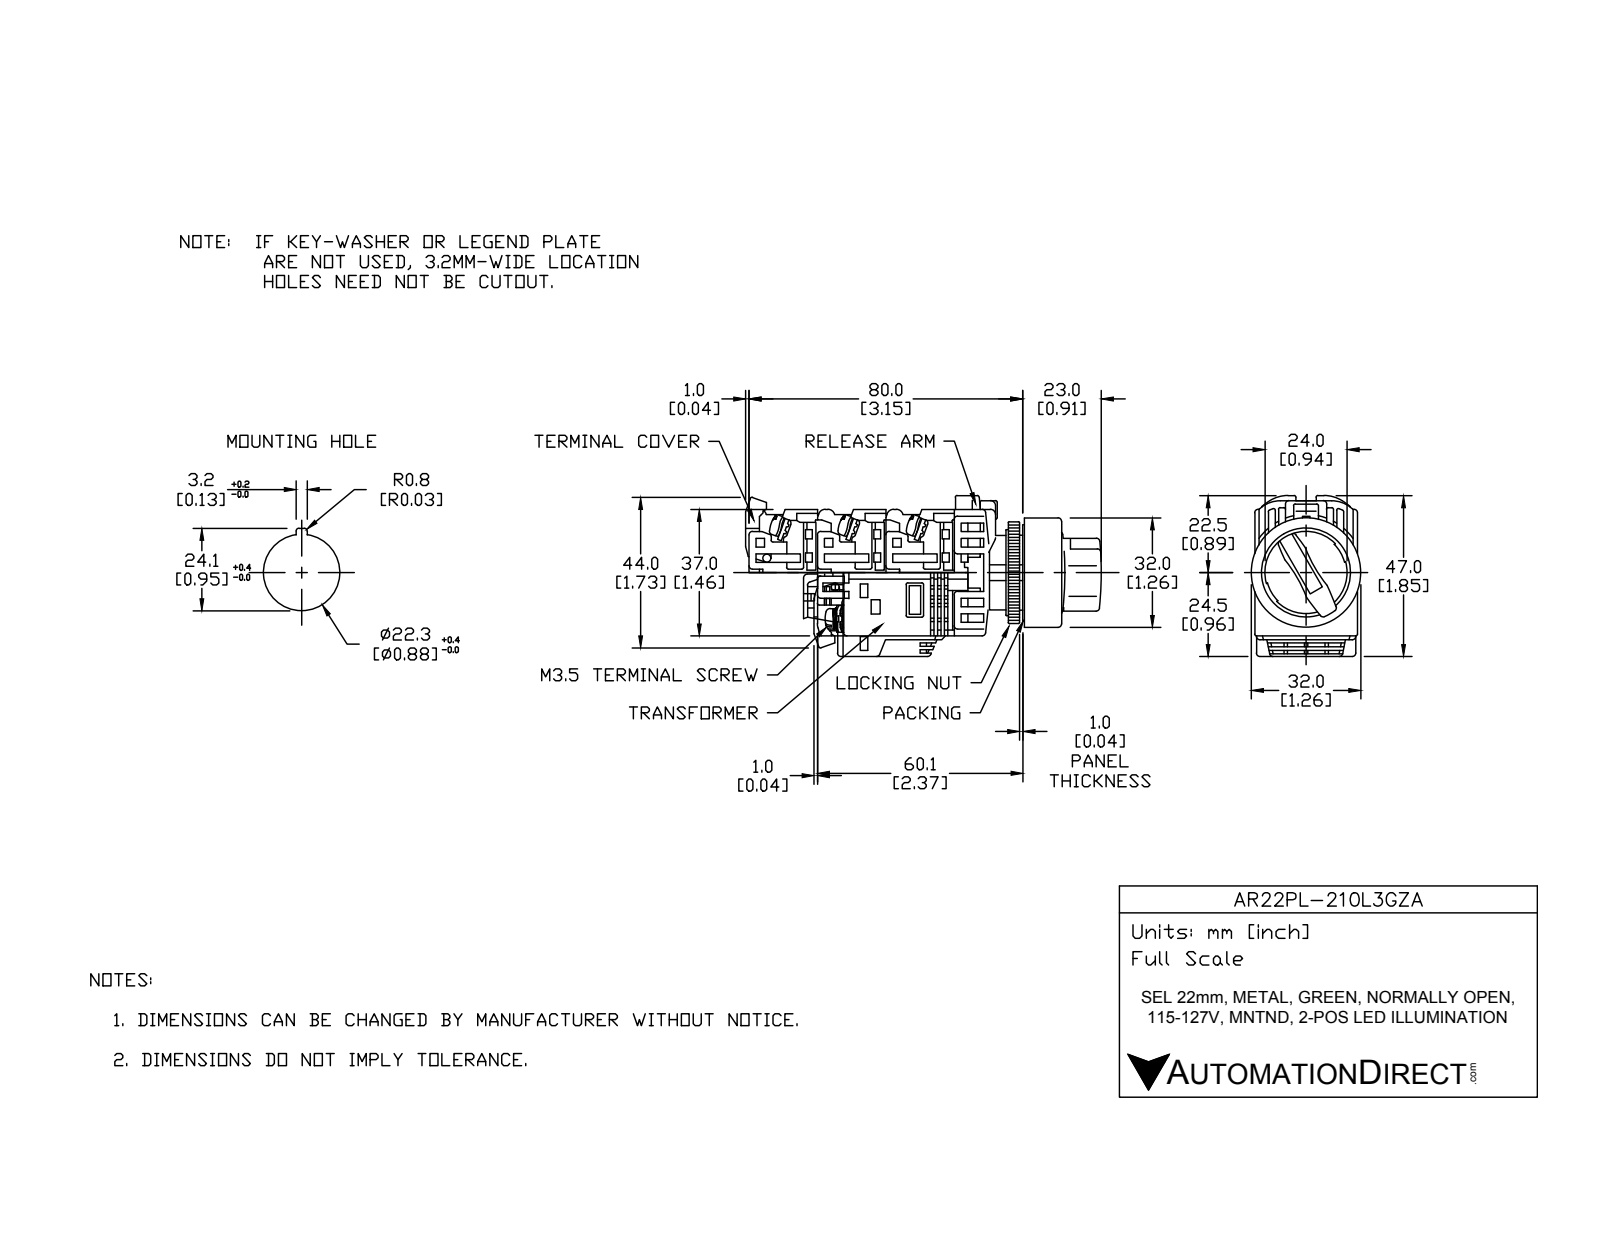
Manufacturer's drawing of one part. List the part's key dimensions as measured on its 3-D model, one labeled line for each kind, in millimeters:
Part name (STEP PRODUCT): AR22PL-210L3GZA
STEP written by: SolidWorks 2017 (AUTOMOTIVE_DESIGN)
Units: millimetres
Bodies: 18 solids, 462 faces (317 planar, 118 cylindrical, 27 other)
Overall size (bounding box): 84.5 × 43.81 × 32
Volume: 48 971 mm³ · Surface area: 26 711 mm²
Round holes (diameter × count): ⌀21.8 ×1, ⌀22 ×1, ⌀25 ×1, ⌀31 ×1
Round bosses / shafts (diameter × count): ⌀5 ×4, ⌀32 ×1, ⌀30.5 ×1, ⌀29.8 ×1, ⌀24 ×1, ⌀21.75 ×1, ⌀17 ×1
Partial cylindrical surfaces — rounded edges, fillets, slot ends (radius × count): R0.5 ×39, R1.75 ×8, R1 ×6, R5 ×4, R4 ×2, R12 ×1, R16.59 ×1, R17.59 ×1
Main face-to-face distances: 1, 18, 29, 20, 3, 28.5, 0.5, 2, 21, 10
